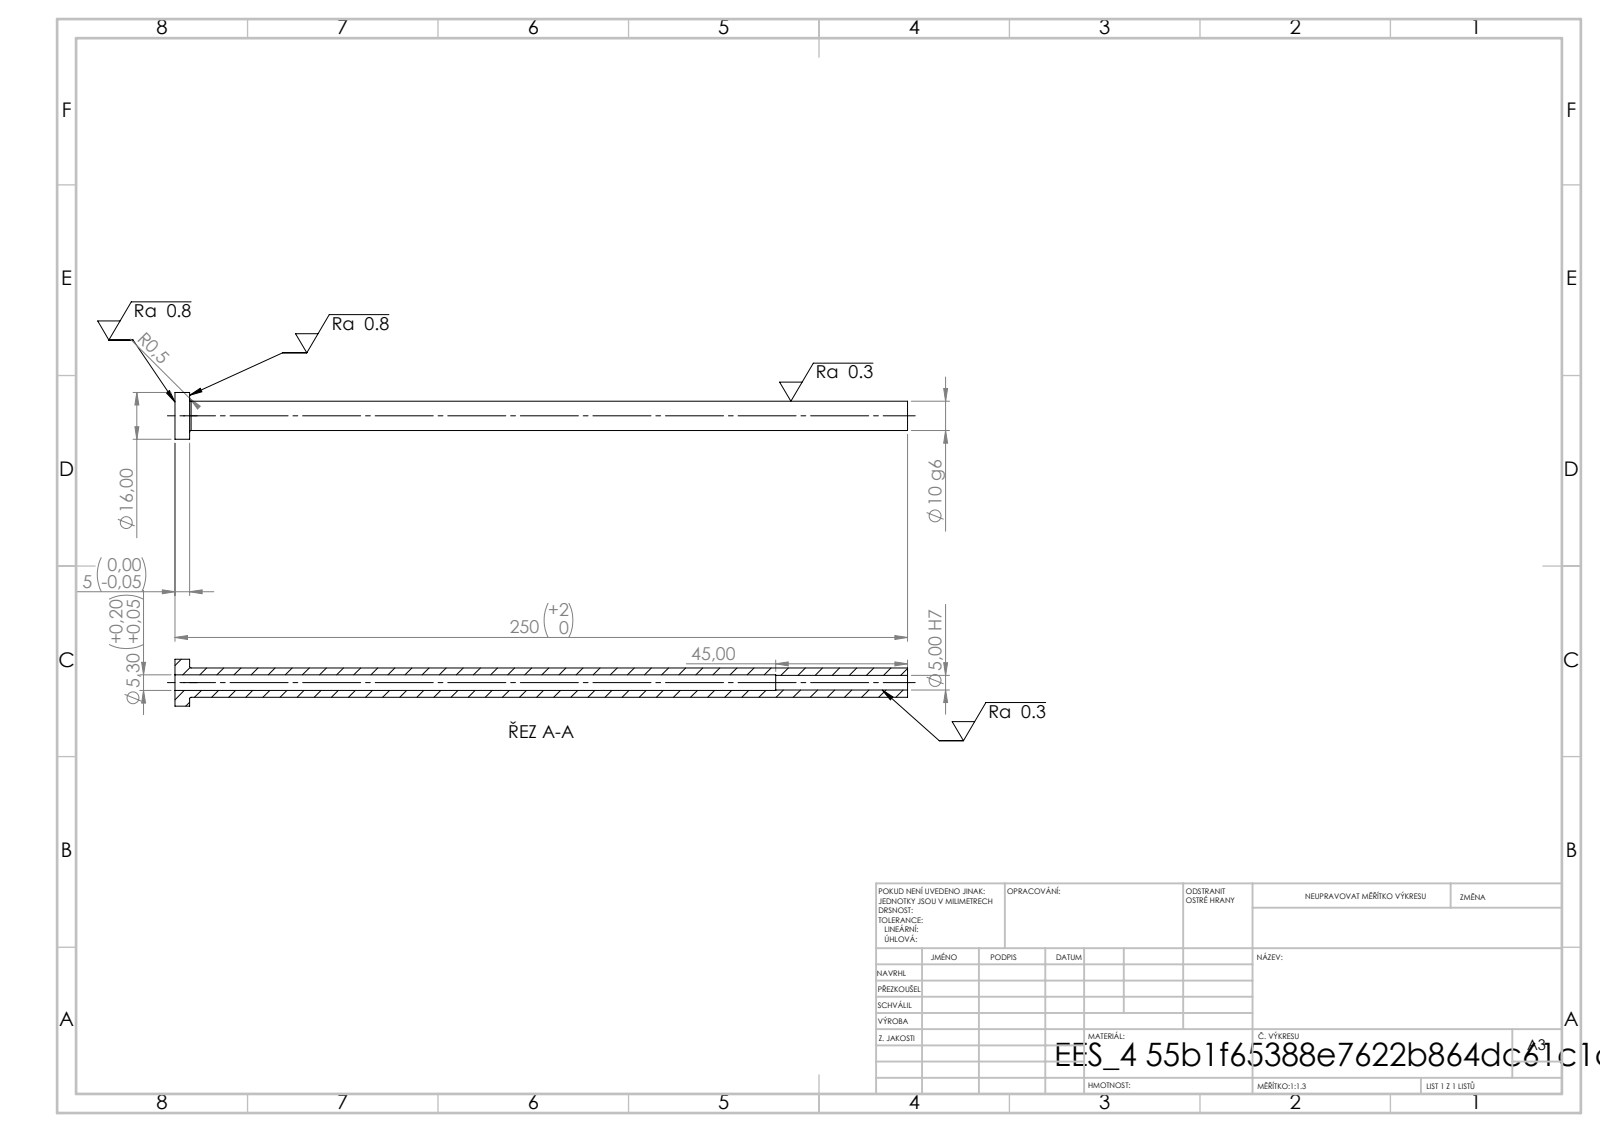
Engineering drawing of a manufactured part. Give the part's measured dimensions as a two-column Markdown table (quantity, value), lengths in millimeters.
| quantity | value |
| --- | --- |
| STEP written by | SolidWorks 2019 (CONFIG_CONTROL_DESIGN) |
| units | millimeters |
| bodies | 1 solid, 14 faces (4 planar, 8 cylindrical, 2 other) |
| overall size | 250 × 16 × 16 |
| volume | 14 843 mm³ |
| surface area | 12 425 mm² |
| round holes (diameter × count) | 5 × 1, 5.3 × 1 |
| round bosses / shafts (diameter × count) | 16 × 1, 10 × 1 |
| main face-to-face distances | 5, 250, 245, 205, 200, 45 |
